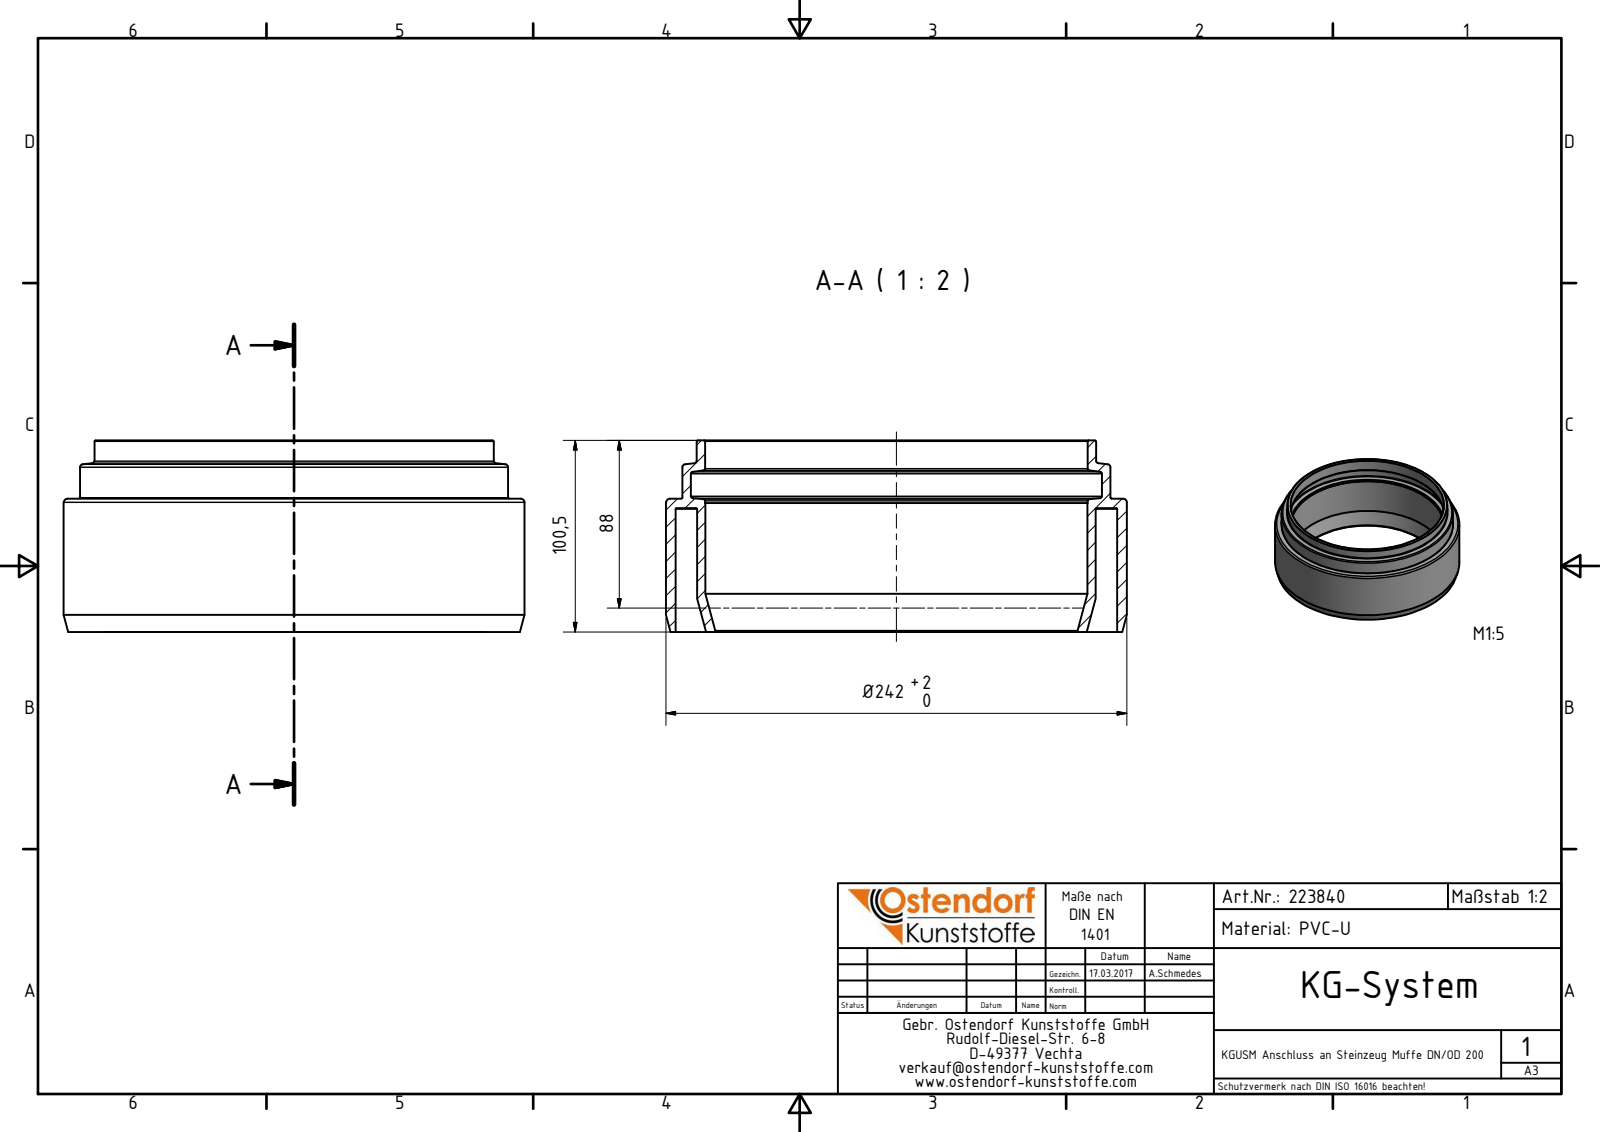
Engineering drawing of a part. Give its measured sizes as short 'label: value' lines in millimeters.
name: 223840 KGUSM Anschluss an Steinzeugrohr-Muffe DN_OD 200
written by: Autodesk Inventor 2016 (AUTOMOTIVE_DESIGN)
unit: mm
bodies: 1 solid, 35 faces (6 planar, 11 cylindrical, 18 other)
size: 242 × 242 × 100.55
volume: 605 201 mm³; area: 261 463 mm²
holes: 1× ⌀190.2, 1× ⌀200, 1× ⌀200.6, 1× ⌀200.9, 1× ⌀216, 1× ⌀232
bosses: 1× ⌀242, 1× ⌀224.8, 1× ⌀209.7, 1× ⌀209.4
face distances: 65, 70, 5, 100.5, 35.5, 30.5, 67.67, 2.67, 2.33, 32.83
